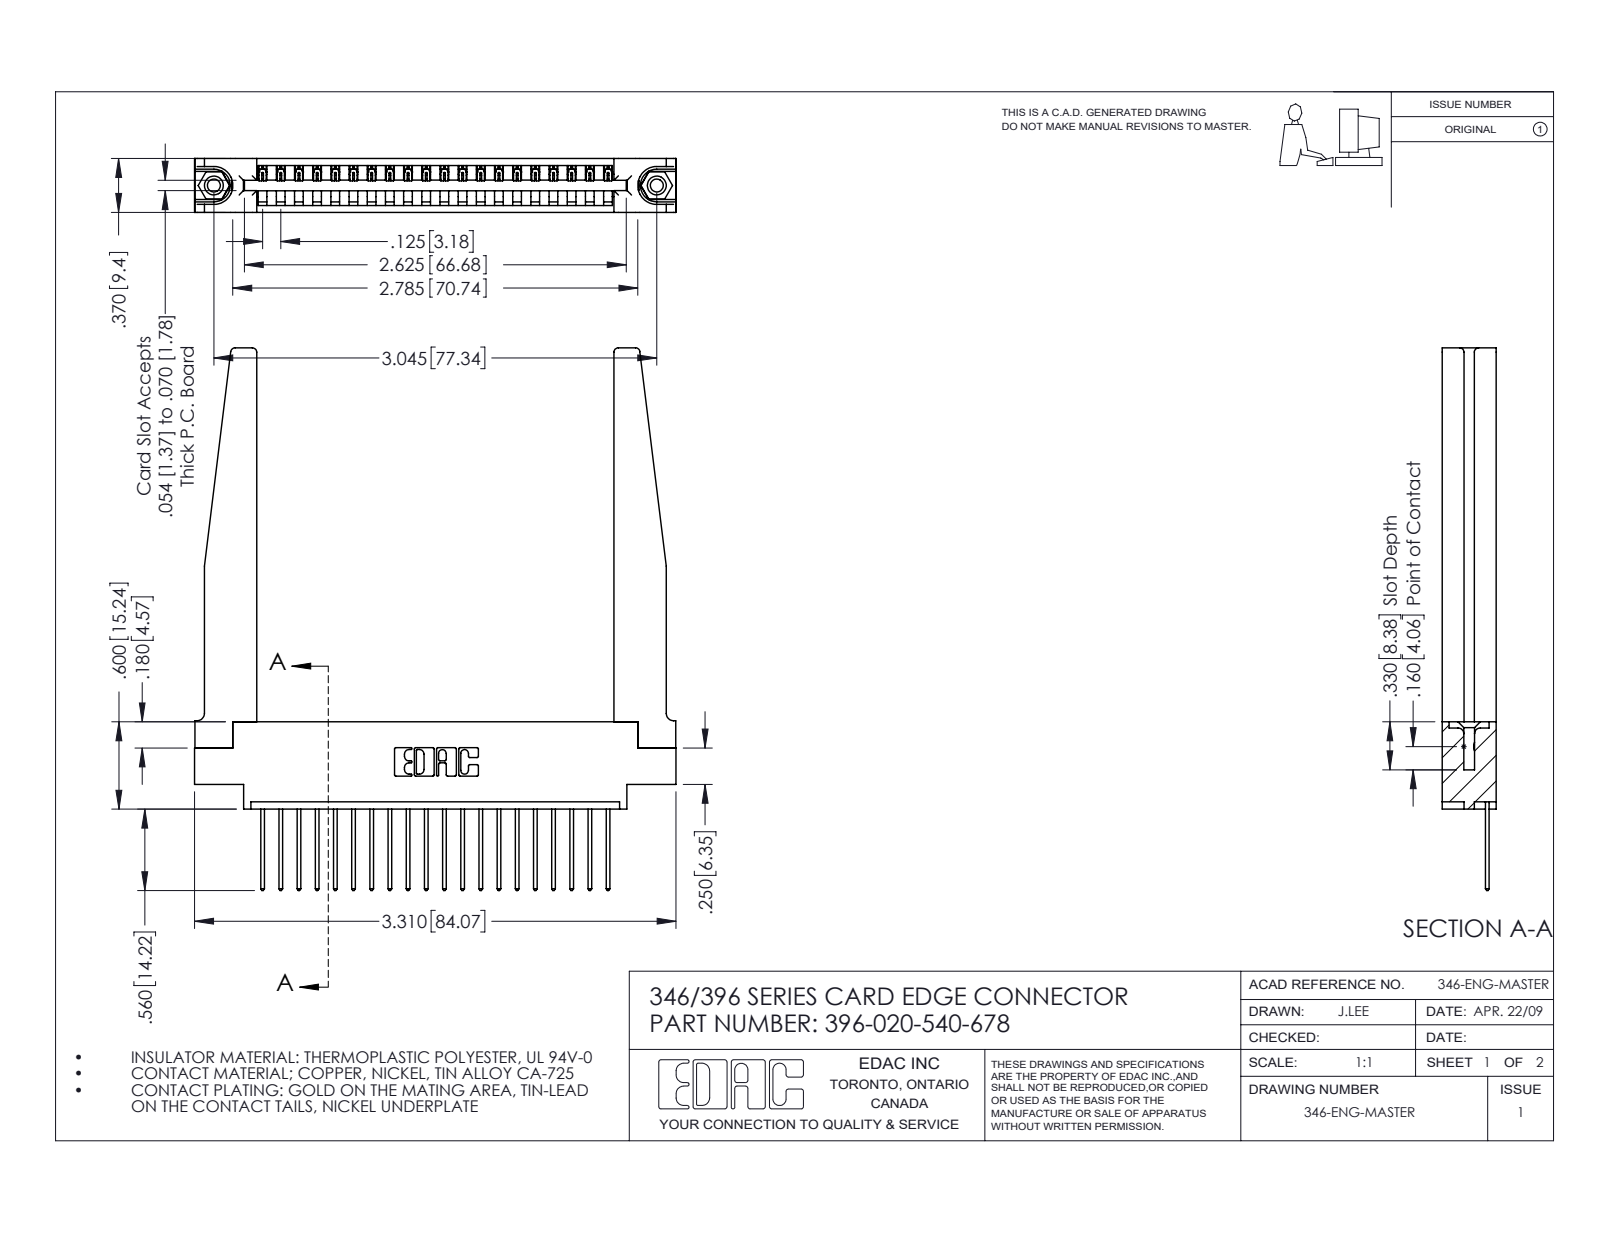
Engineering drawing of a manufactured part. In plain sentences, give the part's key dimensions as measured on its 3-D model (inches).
The part is named "346-220-078_345-220-078; 345-292-001_345-293-140; 396-020-540-678; 346 Part_0.170 Offset - 0.156 Dia-TH (+1 more)". Its 3-D file was written by "SolidWorks 2016 (CONFIG_CONTROL_DESIGN)". It is 25 solids with 1520 faces: 1022 planar, 446 cylindrical and 52 other. Overall it measures 3.73 by 3.31 by 0.37 inches. Its volume is 0.896 cubic inches and its surface area 25.37 square inches. Round holes: 2 of diameter 0.089, 2 of diameter 0.125, 2 of diameter 0.156, 1 of diameter 0.064. Round bosses or shafts: 2 of diameter 0.155. Partial cylindrical surfaces (rounded edges, fillets, slot ends): 40 of radius 0.006, 40 of radius 0.01, 22 of radius 0.01, 8 of radius 0.03, 6 of radius 0.007, 6 of radius 0.031, 3 of radius 0.026, 2 of radius 0.031. The main face-to-face distances are 0.37, 0.072, 0.048, 0.322, 0.15, 0.148, 0.25, 0.298, 0.025, 0.102. The hole center spacings are 0.246, 2.837, 3.045.
